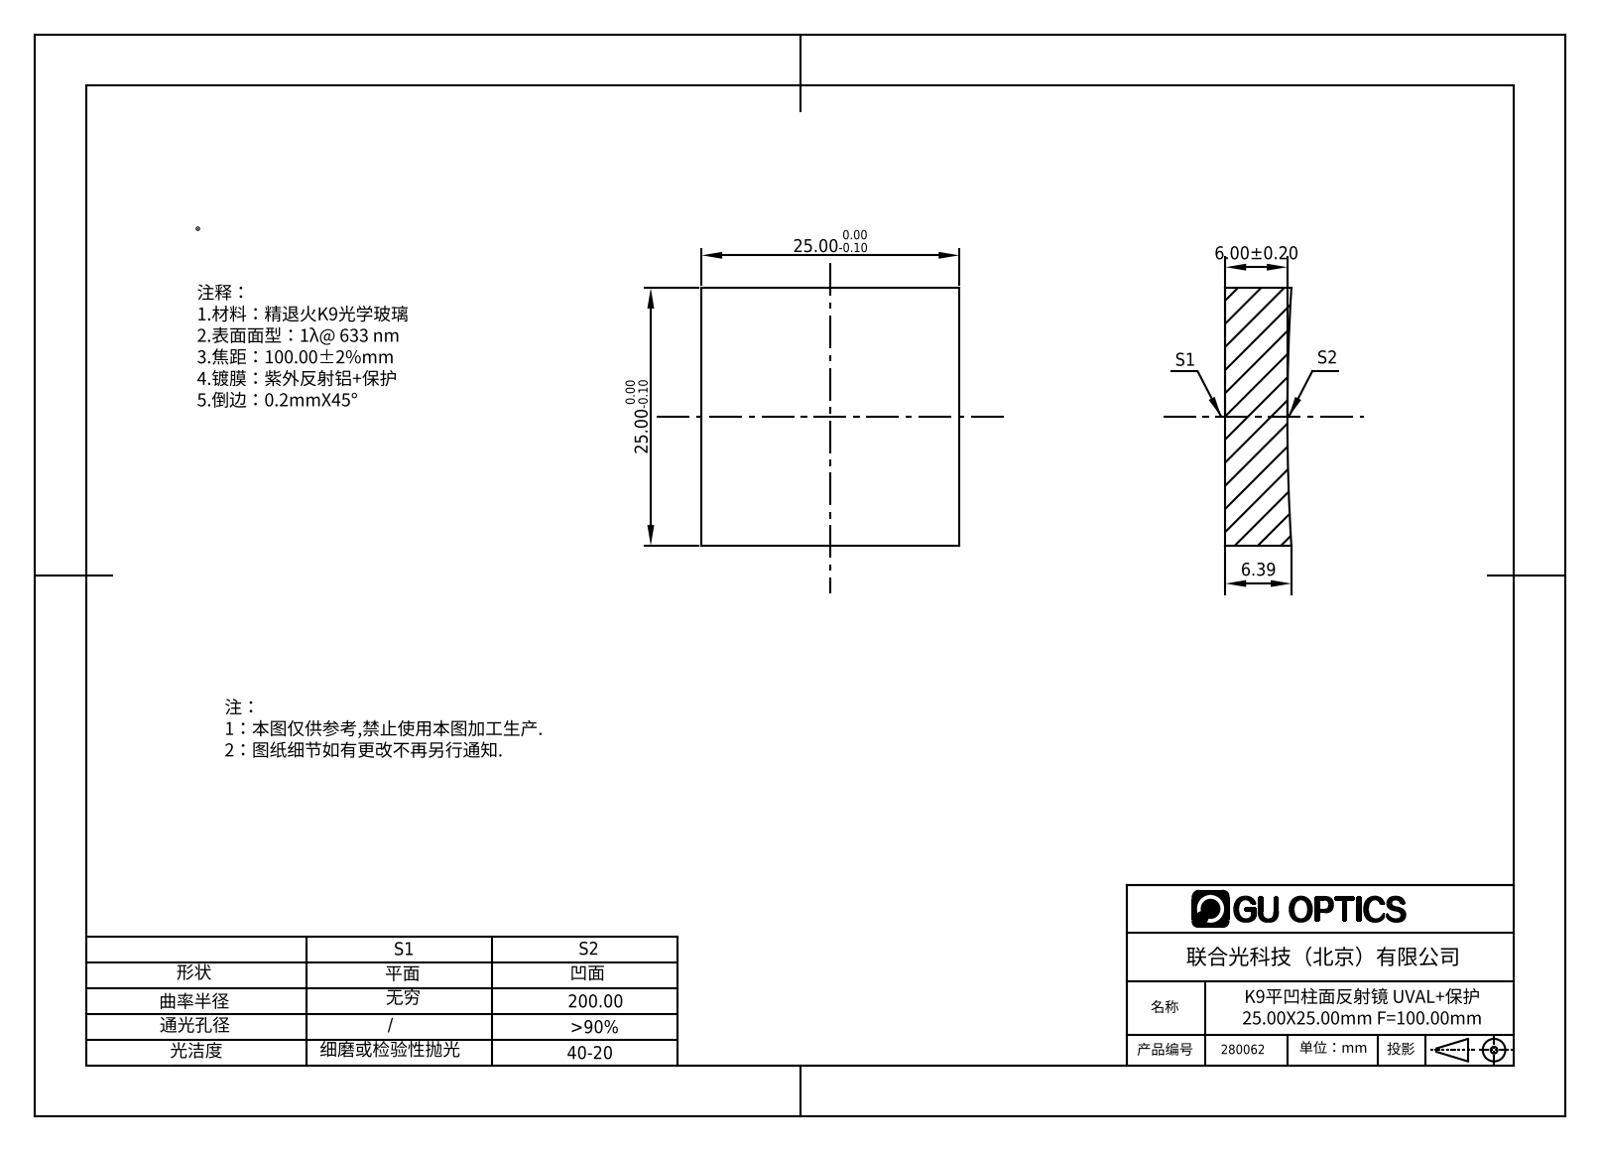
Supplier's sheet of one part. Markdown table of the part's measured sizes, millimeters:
| quantity | value |
| --- | --- |
| part name | 280018 |
| STEP written by | SolidWorks 2016 (AUTOMOTIVE_DESIGN) |
| units | millimeters |
| bodies | 1 solid, 7 faces (5 planar, 2 cylindrical, 0 other) |
| overall size | 25 × 25 × 6.39 |
| volume | 3 831 mm³ |
| surface area | 1 876 mm² |
| partial cylindrical surfaces (radius × count) | 200 × 1 |
| main face-to-face distances | 25 |
